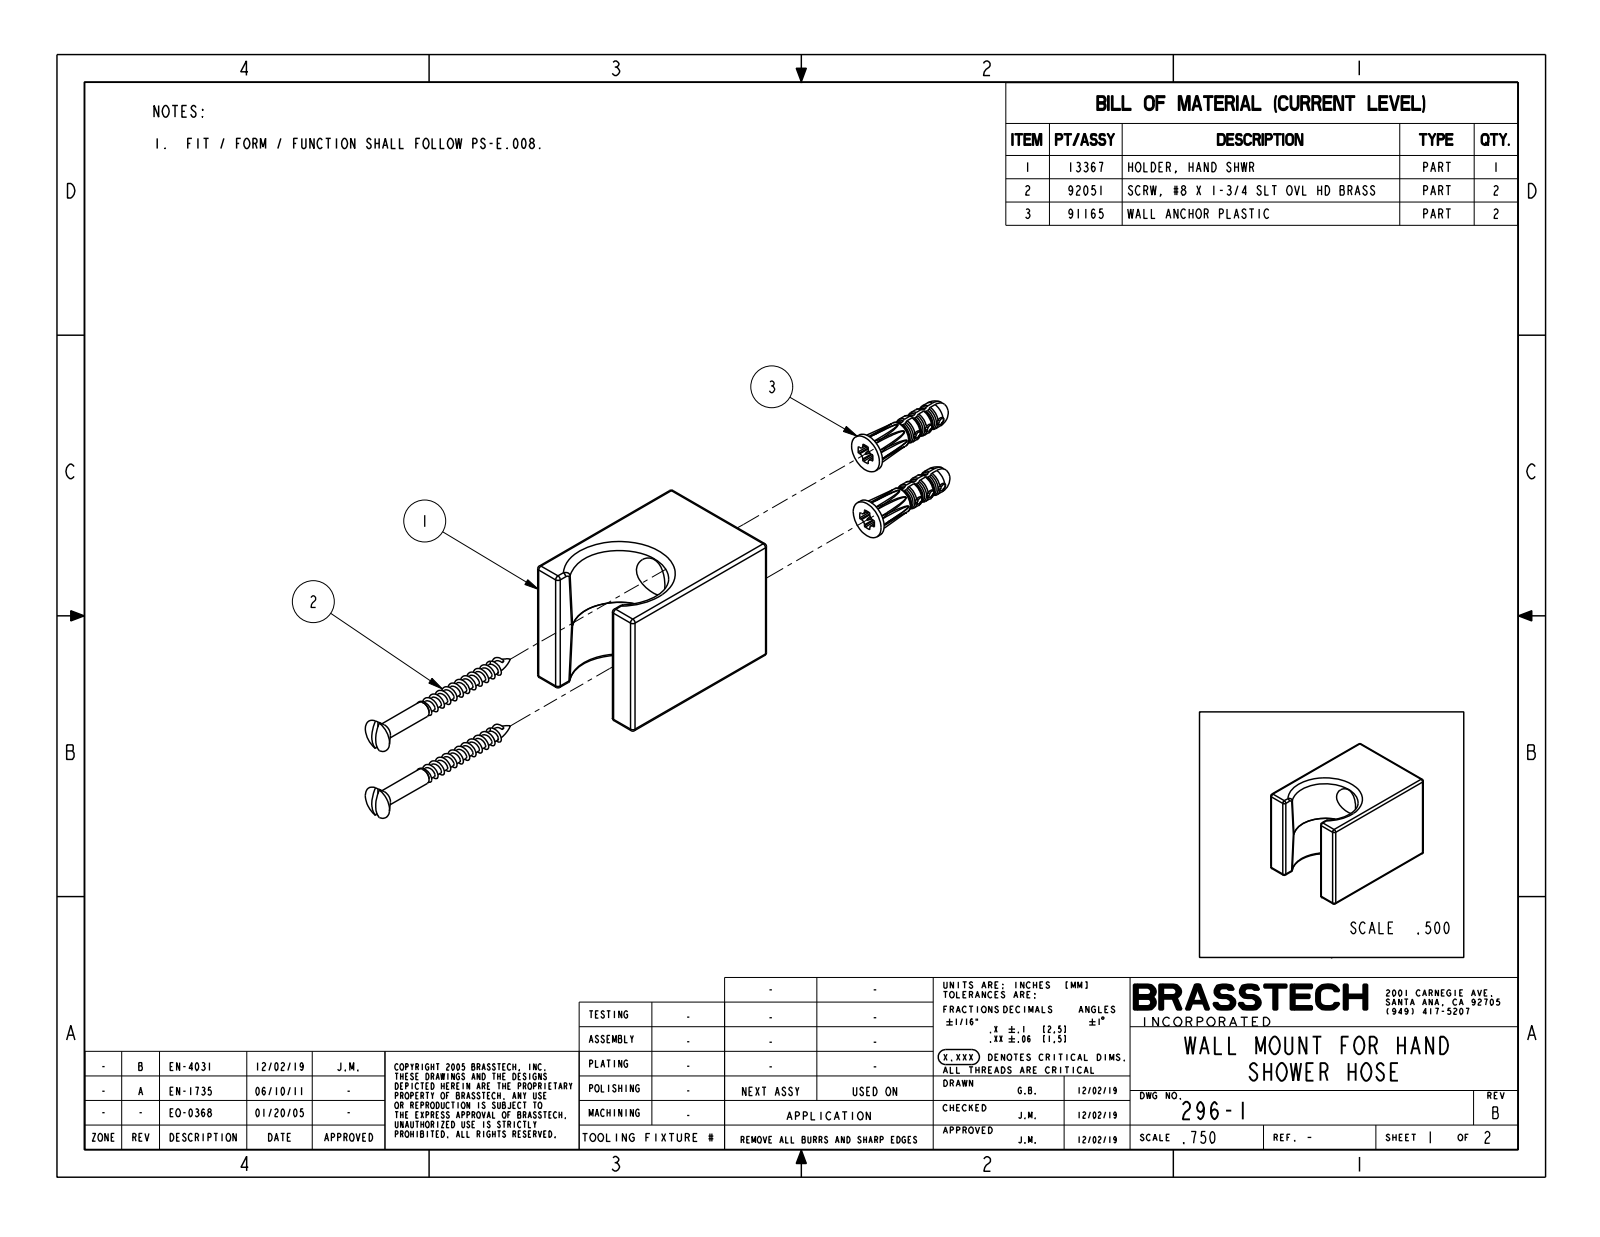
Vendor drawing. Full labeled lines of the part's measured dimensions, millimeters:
Part name (STEP PRODUCT): 296-1_WEB
STEP written by: PRO/ENGINEER BY PARAMETRIC TECHNOLOGY CORPORATION, 2009300 (CONFIG_CONTROL_DESIGN)
Units: millimetres
Bodies: 0 solids, 62 faces (9 planar, 28 cylindrical, 25 other)
Overall size (bounding box): 44.5 × 31.8 × 31.8
Round holes (diameter × count): ⌀4.8 ×2, ⌀9.3 ×2
Partial cylindrical surfaces — rounded edges, fillets, slot ends (radius × count): R1 ×18
Main face-to-face distances: 31.8, 31.8, 44.5, 7.6, 24.1, 16.5
Hole centre spacings: 19.1
